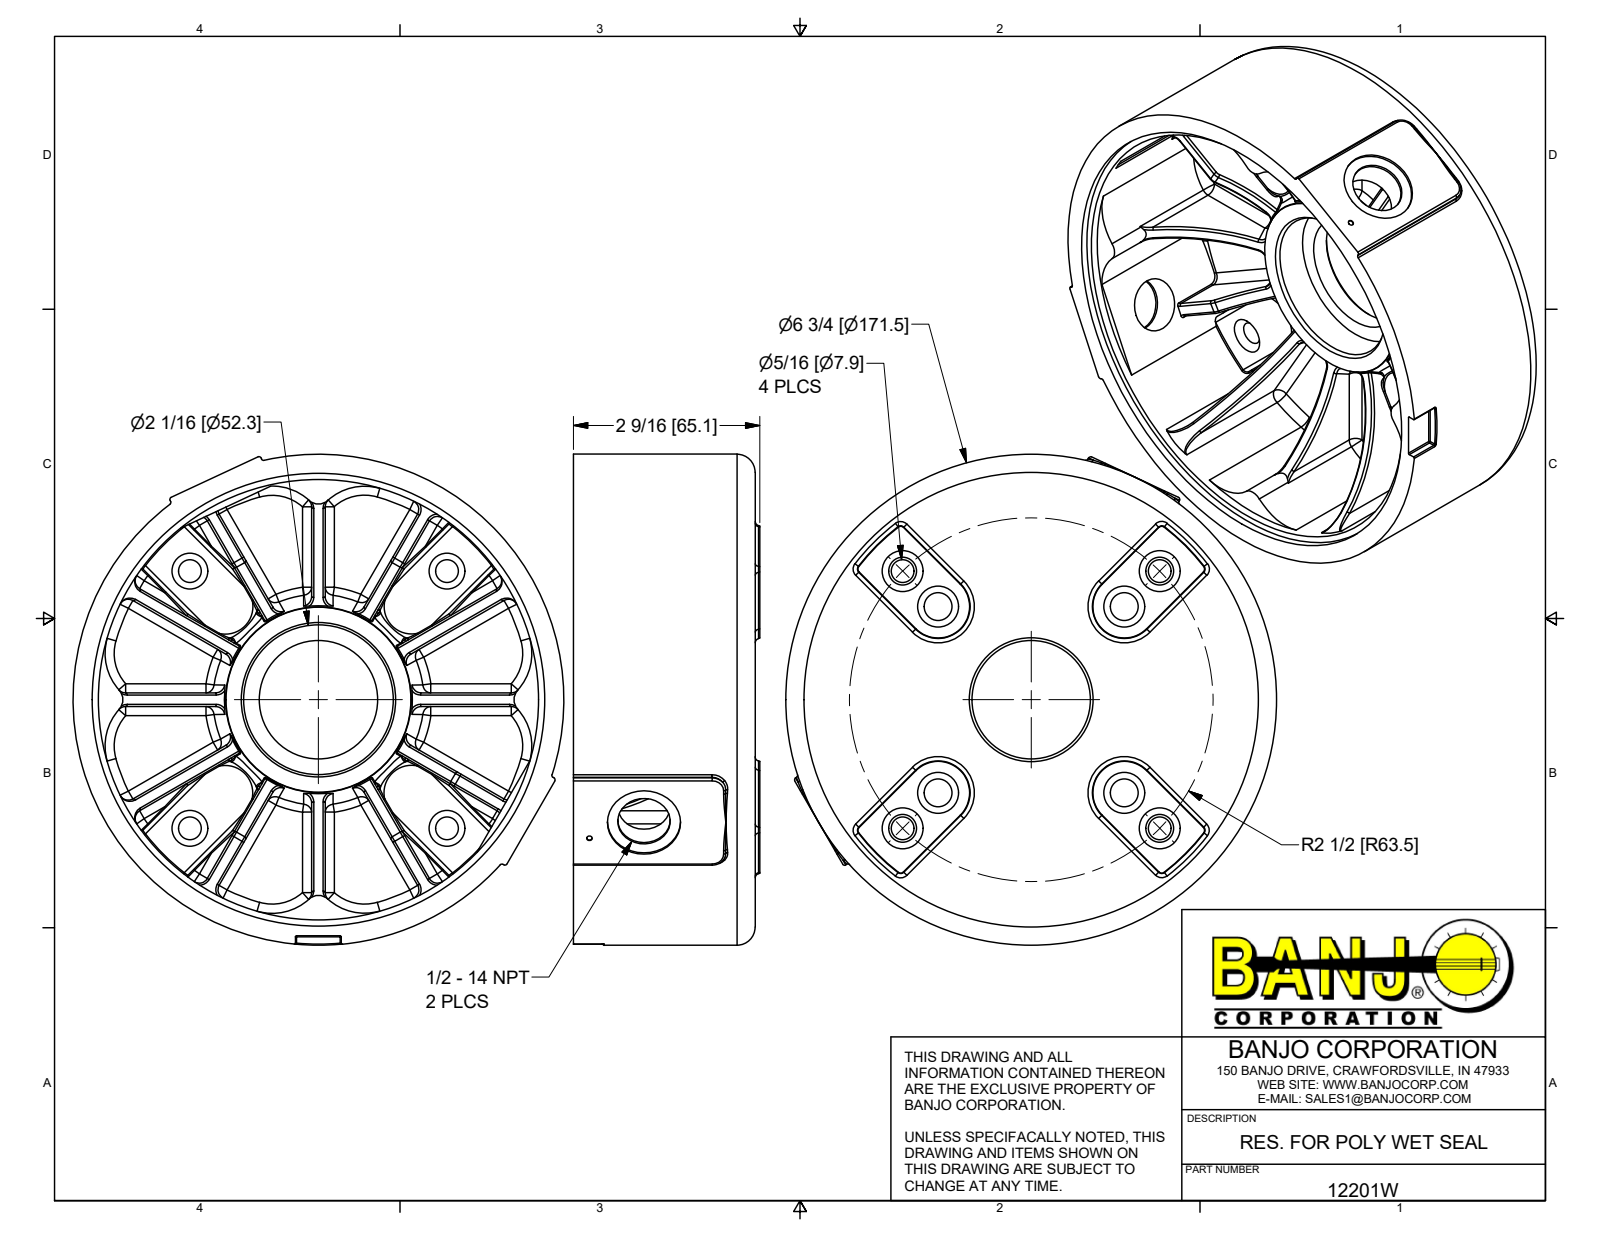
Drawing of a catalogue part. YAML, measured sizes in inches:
part_name: "12201W; 12201WZ; 12201WY; 12201WX"
step_written_by: "Autodesk Inventor 2017 (AUTOMOTIVE_DESIGN)"
units: inches
bodies: {solids: 1, faces: 667, planar: 102, cylindrical: 200, other: 365}
overall_size: [6.75, 6.75, 2.563]
volume: 33.89
surface_area: 190
round_holes:
  - {diameter: 0.561, count: 8}
  - {diameter: 0.313, count: 4}
  - {diameter: 0.719, count: 2}
  - {diameter: 1.005, count: 2}
  - {diameter: 0.075, count: 1}
  - {diameter: 1.63, count: 1}
  - {diameter: 2.06, count: 1}
  - {diameter: 6.05, count: 1}
  - {diameter: 6.224, count: 1}
round_bosses_or_shafts:
  - {diameter: 0.381, count: 8}
  - {diameter: 6.75, count: 1}
partial_cylinders:
  - {radius: 0.125, count: 41}
  - {radius: 0.015, count: 37}
  - {radius: 0.06, count: 24}
  - {radius: 0.03, count: 16}
  - {radius: 2.5, count: 12}
  - {radius: 0.187, count: 8}
  - {radius: 0.75, count: 8}
face_to_face_distances: [0.187, 0.375, 2.499, 2.124, 0.437, 0.064, 0.439, 2.563, 0.689, 0.625]
hole_center_spacings: [3.087, 0.69, 1.81, 2.5, 2.56, 3.535, 4.31, 3.62]
